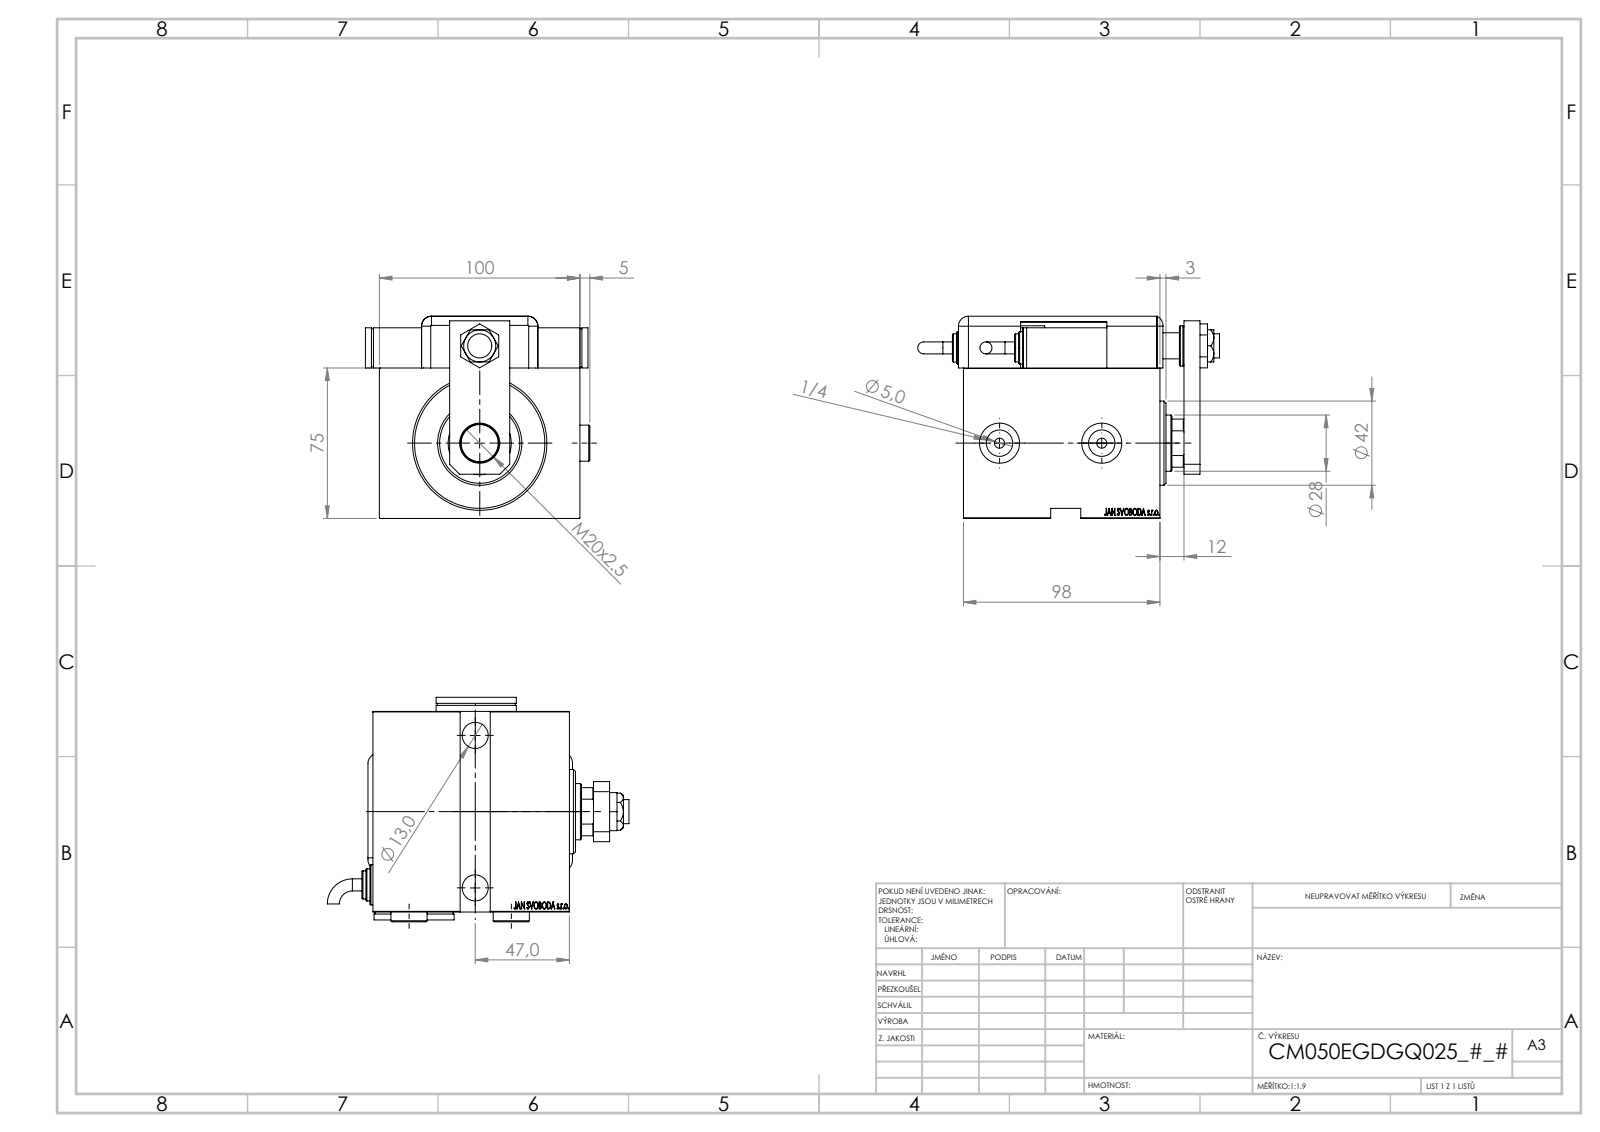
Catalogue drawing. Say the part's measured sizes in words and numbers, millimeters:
The part is named "MAGNETIC SWITCH Q; V450CM_E_Body; SWITCH Q; V450CM_E_VCP (+7 more)". Its 3-D file was written by "SolidWorks 2019 (CONFIG_CONTROL_DESIGN)". It is 15 solids with 1286 faces: 650 planar, 115 cylindrical and 521 other. Overall it measures 150.46 by 111.9 by 100.8 millimeters. Its volume is 814 074 cubic millimeters and its surface area 155 611 square millimeters. Round holes: 3 of diameter 13, 3 of diameter 20, 2 of diameter 4, 2 of diameter 5, 2 of diameter 8, 2 of diameter 13.16, 2 of diameter 19, 1 of diameter 12, 1 of diameter 14, 1 of diameter 18.5, 1 of diameter 28, 1 of diameter 31.5. Round bosses or shafts: 3 of diameter 20, 2 of diameter 18, 2 of diameter 16, 2 of diameter 14, 2 of diameter 6, 1 of diameter 52, 1 of diameter 42. Partial cylindrical surfaces (rounded edges, fillets, slot ends): 9 of radius 5, 1 of radius 10, 1 of radius 13.5. The main face-to-face distances are 3, 75, 98, 100, 14, 20, 84, 79, 100.8, 25.8. The hole center spacings are 47.2, 61.22, 20, 48.5, 51, 76.
